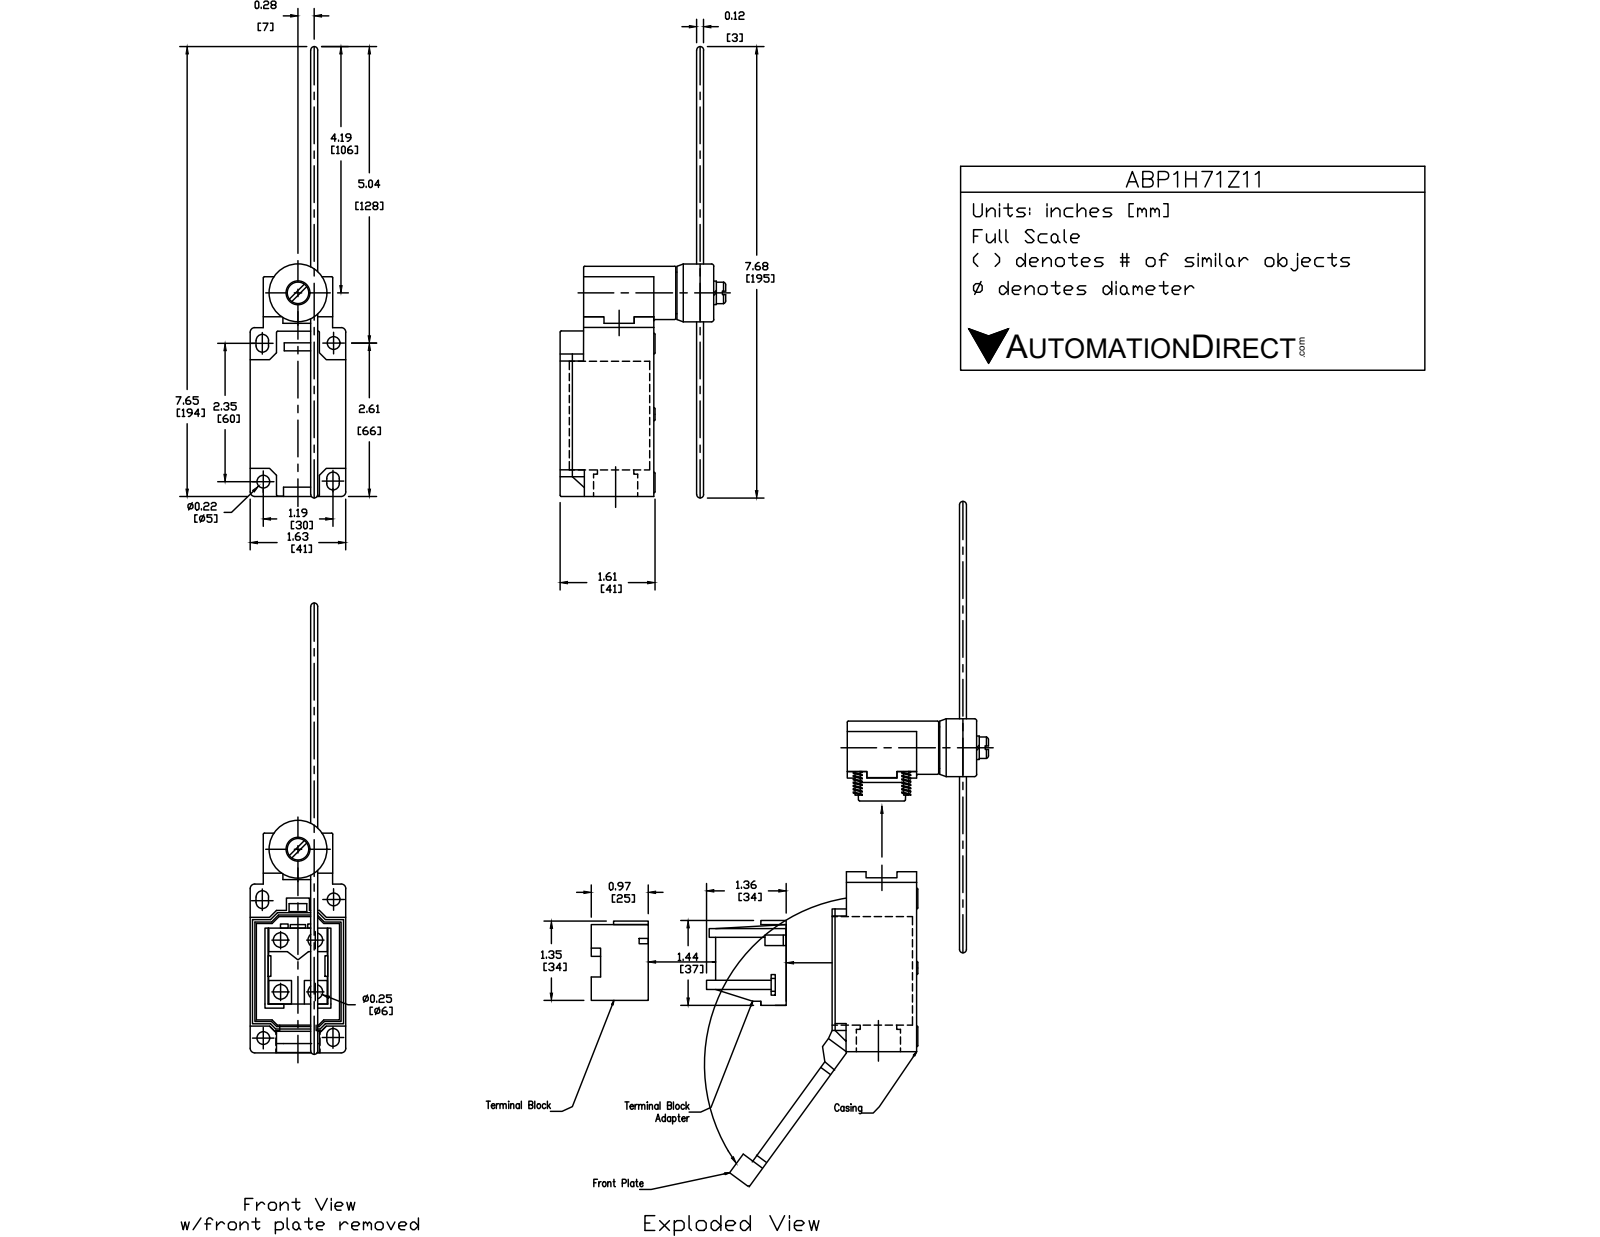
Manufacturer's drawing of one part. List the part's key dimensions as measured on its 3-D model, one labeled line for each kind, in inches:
Part name (STEP PRODUCT): ABP1H71Z11
STEP written by: SolidWorks 2017 (AUTOMOTIVE_DESIGN)
Units: inches
Bodies: 7 solids, 219 faces (122 planar, 79 cylindrical, 18 other)
Overall size (bounding box): 7.675 × 2.414 × 1.614
Volume: 8.629 in³ · Surface area: 45.01 in²
Round holes (diameter × count): ⌀0.213 ×2, ⌀0.236 ×1, ⌀0.551 ×1, ⌀0.669 ×1, ⌀0.748 ×1
Round bosses / shafts (diameter × count): ⌀0.354 ×5, ⌀0.984 ×1, ⌀0.906 ×1, ⌀0.709 ×1, ⌀0.394 ×1, ⌀0.118 ×1
Partial cylindrical surfaces — rounded edges, fillets, slot ends (radius × count): R0.02 ×16, R0.079 ×4, R0.106 ×4, R0.453 ×1, R0.472 ×1
Main face-to-face distances: 1.614, 1.565, 1.181, 0.217, 1.398, 2.972, 0.384, 0.098, 3.071, 0.624
Hole centre spacings: 1.042, 1.376, 2.641, 3.274
